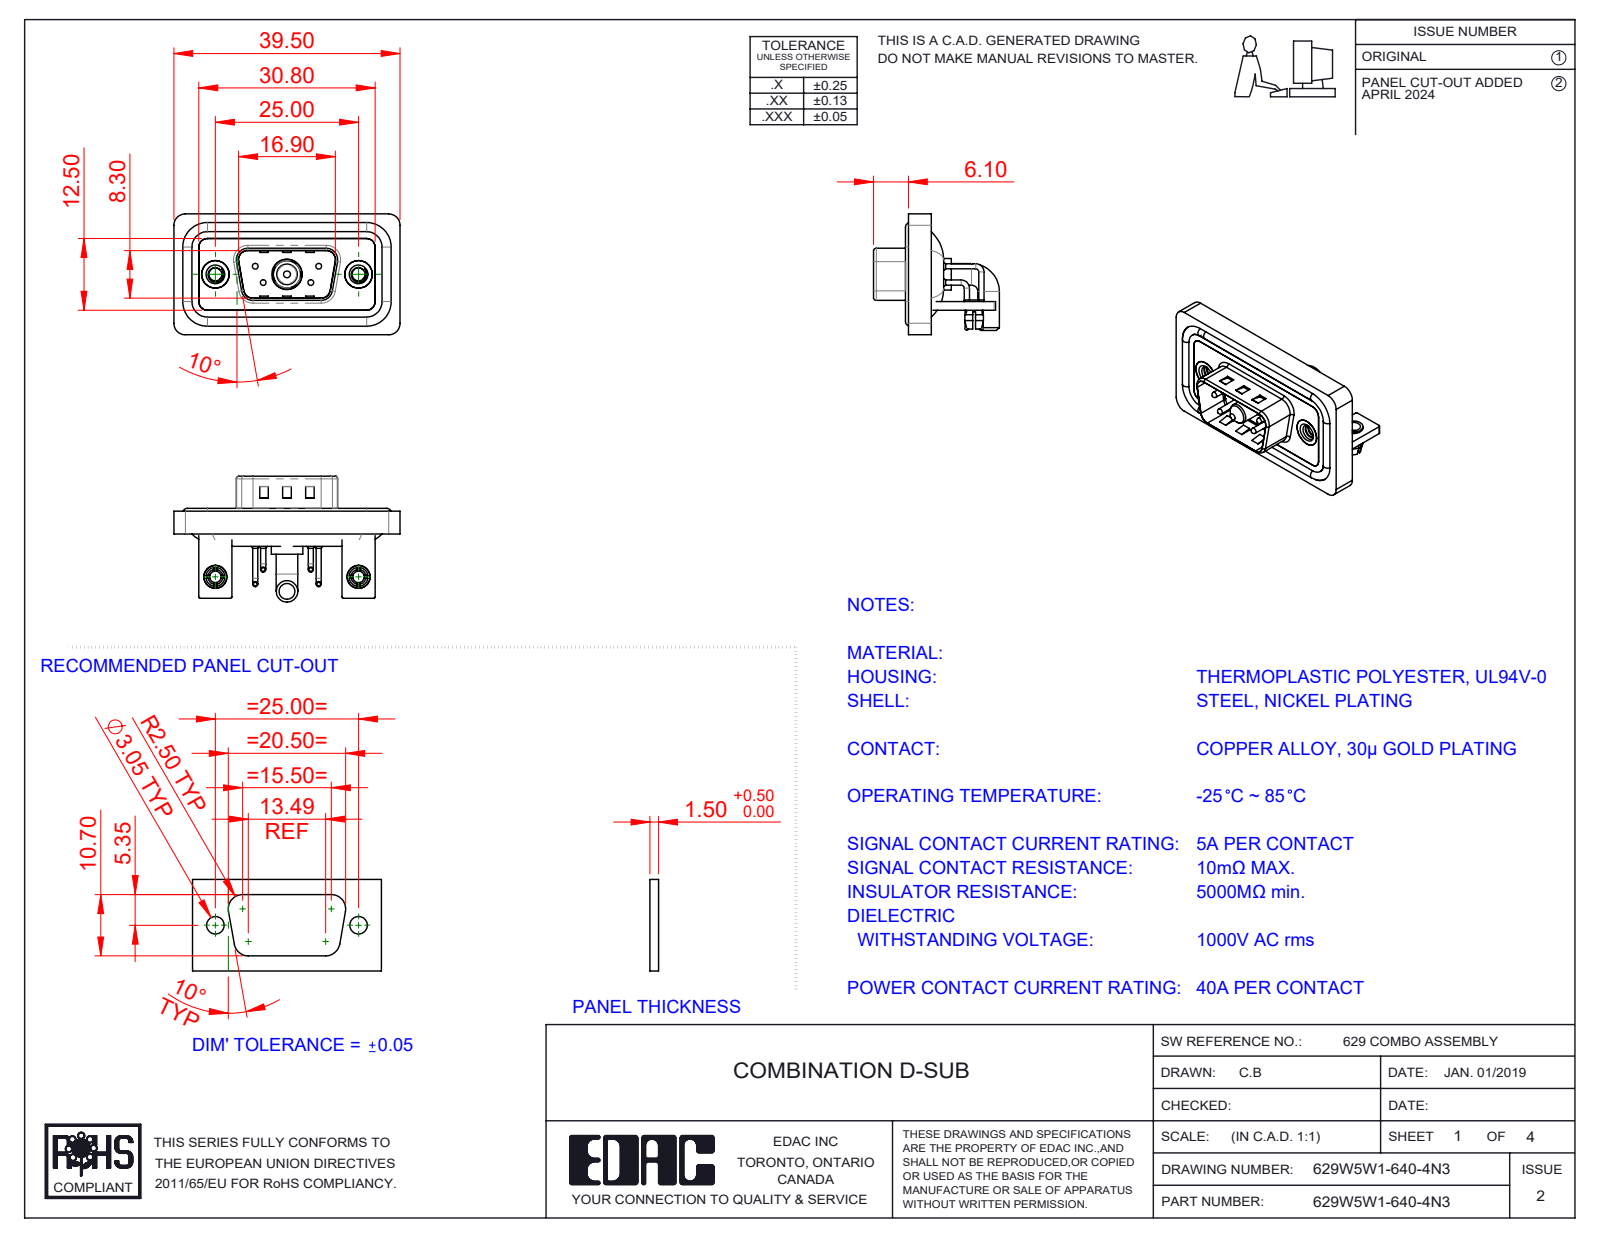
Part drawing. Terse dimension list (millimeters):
name: 629Combo Threaded Rivet_3; 629Combo Contact Row 1; 629Combo Housing_5W1; 629W5W1-640-4N3 (+7 more)
written by: SolidWorks 2023 (CONFIG_CONTROL_DESIGN)
unit: mm
bodies: 17 solids, 1026 faces (479 planar, 395 cylindrical, 152 other)
size: 39.5 × 21.98 × 21.1
volume: 4 863 mm³; area: 8 005 mm²
holes: 6× ⌀2, 4× ⌀0.75, 4× ⌀1.6, 2× ⌀2.26, 2× ⌀2.5, 2× ⌀3.2, 2× ⌀4, 2× ⌀4.8, 2× ⌀5, 1× ⌀4.85, 1× ⌀5.3
bosses: 8× ⌀0.9, 4× ⌀1.6, 4× ⌀1.5, 4× ⌀1, 4× ⌀0.65, 2× ⌀4.9, 2× ⌀4, 2× ⌀3.75
rounds: 19× R2, 18× R1.5, 16× R0.25, 9× R0.5, 8× R1.6, 4× R0.6, 4× R0.65, 4× R0.9
face distances: 0.4, 1.5, 0.8, 2.9, 1.1, 2.1, 1.2, 1.6, 2.5, 3.7
hole spacings: 3.16, 5.72, 7.1, 12.5, 18.1, 25, 4.39, 4.4
